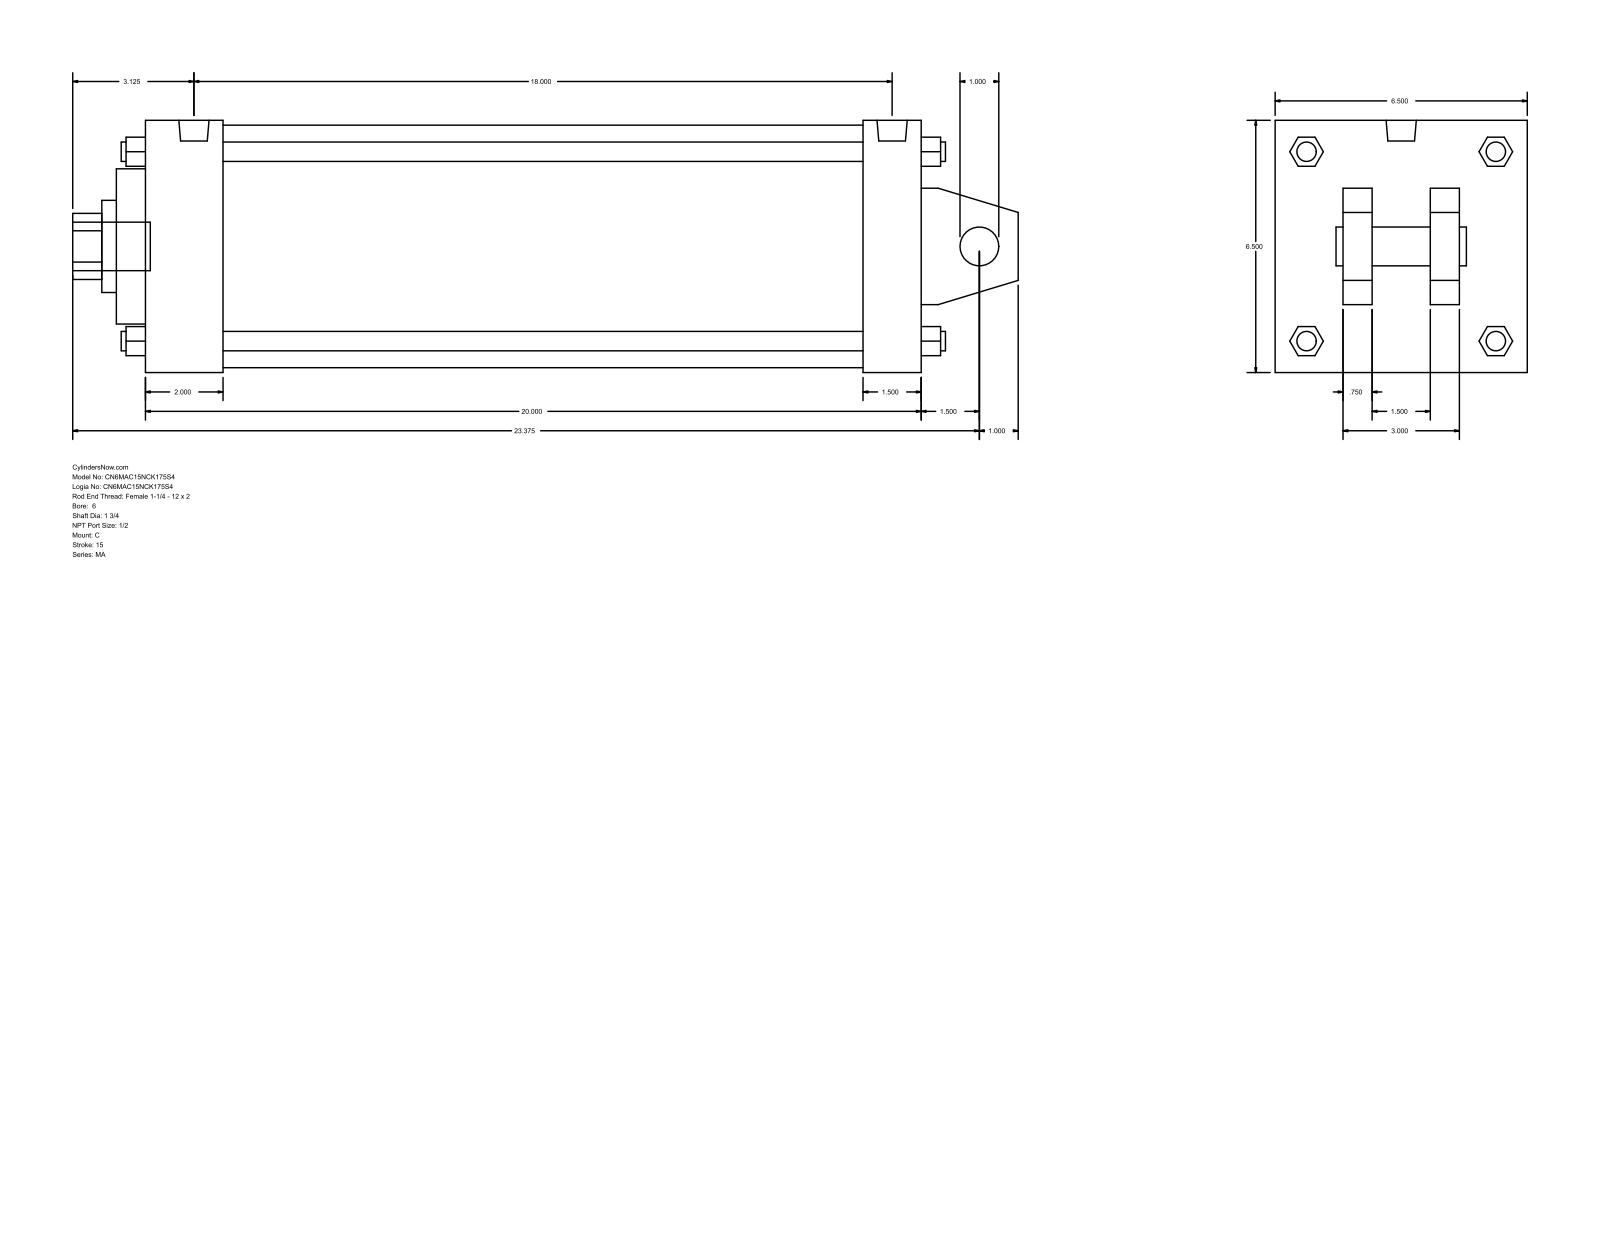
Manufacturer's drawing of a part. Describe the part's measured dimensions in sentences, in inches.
The part is named "MA_C__0600_1.75". Its 3-D file was written by "GSSL Pune (CONFIG_CONTROL_DESIGN)". It is 0 solids with 141 faces: 109 planar, 32 cylindrical and 0 other. Overall it measures 24.375 by 6.5 by 6.5 inches. Round holes: 1 of diameter 1, 1 of diameter 1.75, 1 of diameter 2.375, 1 of diameter 4, 1 of diameter 6.25. Round bosses or shafts: 4 of diameter 0.687, 4 of diameter 0.5, 2 of diameter 0.778, 1 of diameter 1.25. Partial cylindrical surfaces (rounded edges, fillets, slot ends): 1 of radius 0.852. The main face-to-face distances are 6.5, 20, 0.75, 1.5, 2.5, 4, 1.75, 4.75, 2.25, 2.
